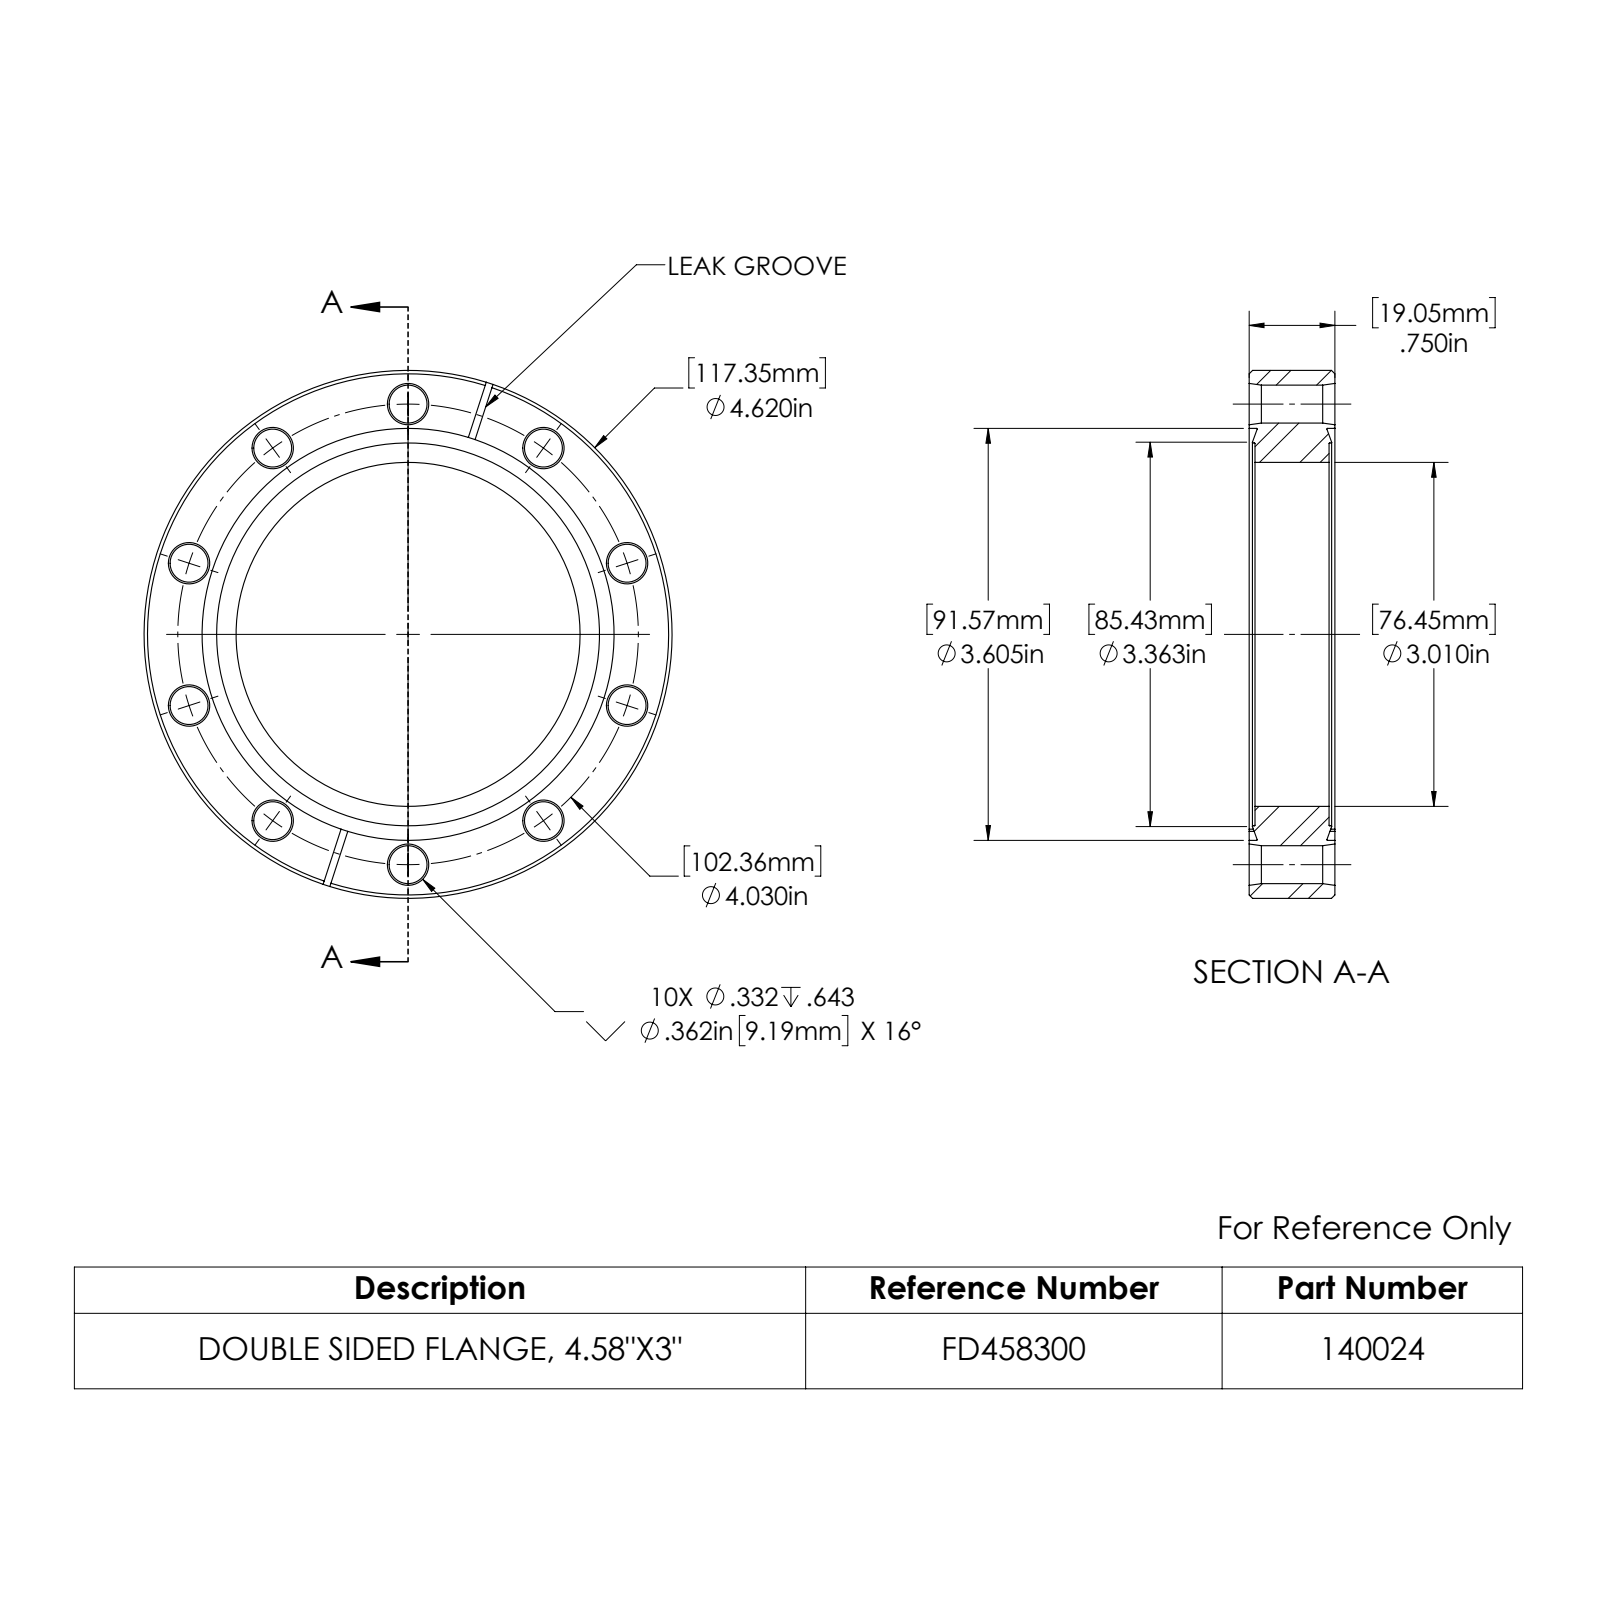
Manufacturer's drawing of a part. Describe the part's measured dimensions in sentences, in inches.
The part is named "140024_A". Its 3-D file was written by "SolidWorks 2022 (CONFIG_CONTROL_DESIGN)". It is 1 solid with 112 faces: 14 planar, 36 cylindrical and 62 other. Overall it measures 4.62 by 4.62 by 0.75 inches. Its volume is 6.231 cubic inches and its surface area 44.2 square inches. Round holes: 10 of diameter 0.332, 1 of diameter 3.01, 1 of diameter 3.35, 1 of diameter 3.605. Round bosses or shafts: 1 of diameter 4.62. Partial cylindrical surfaces (rounded edges, fillets, slot ends): 4 of radius 1.25. The main face-to-face distances are 0.75, 0.051, 0.699, 0.648, 0.062. The hole center spacings are 1.246, 2.015, 3.261, 3.833, 1.245, 2.015, 2.369, 2.369.
